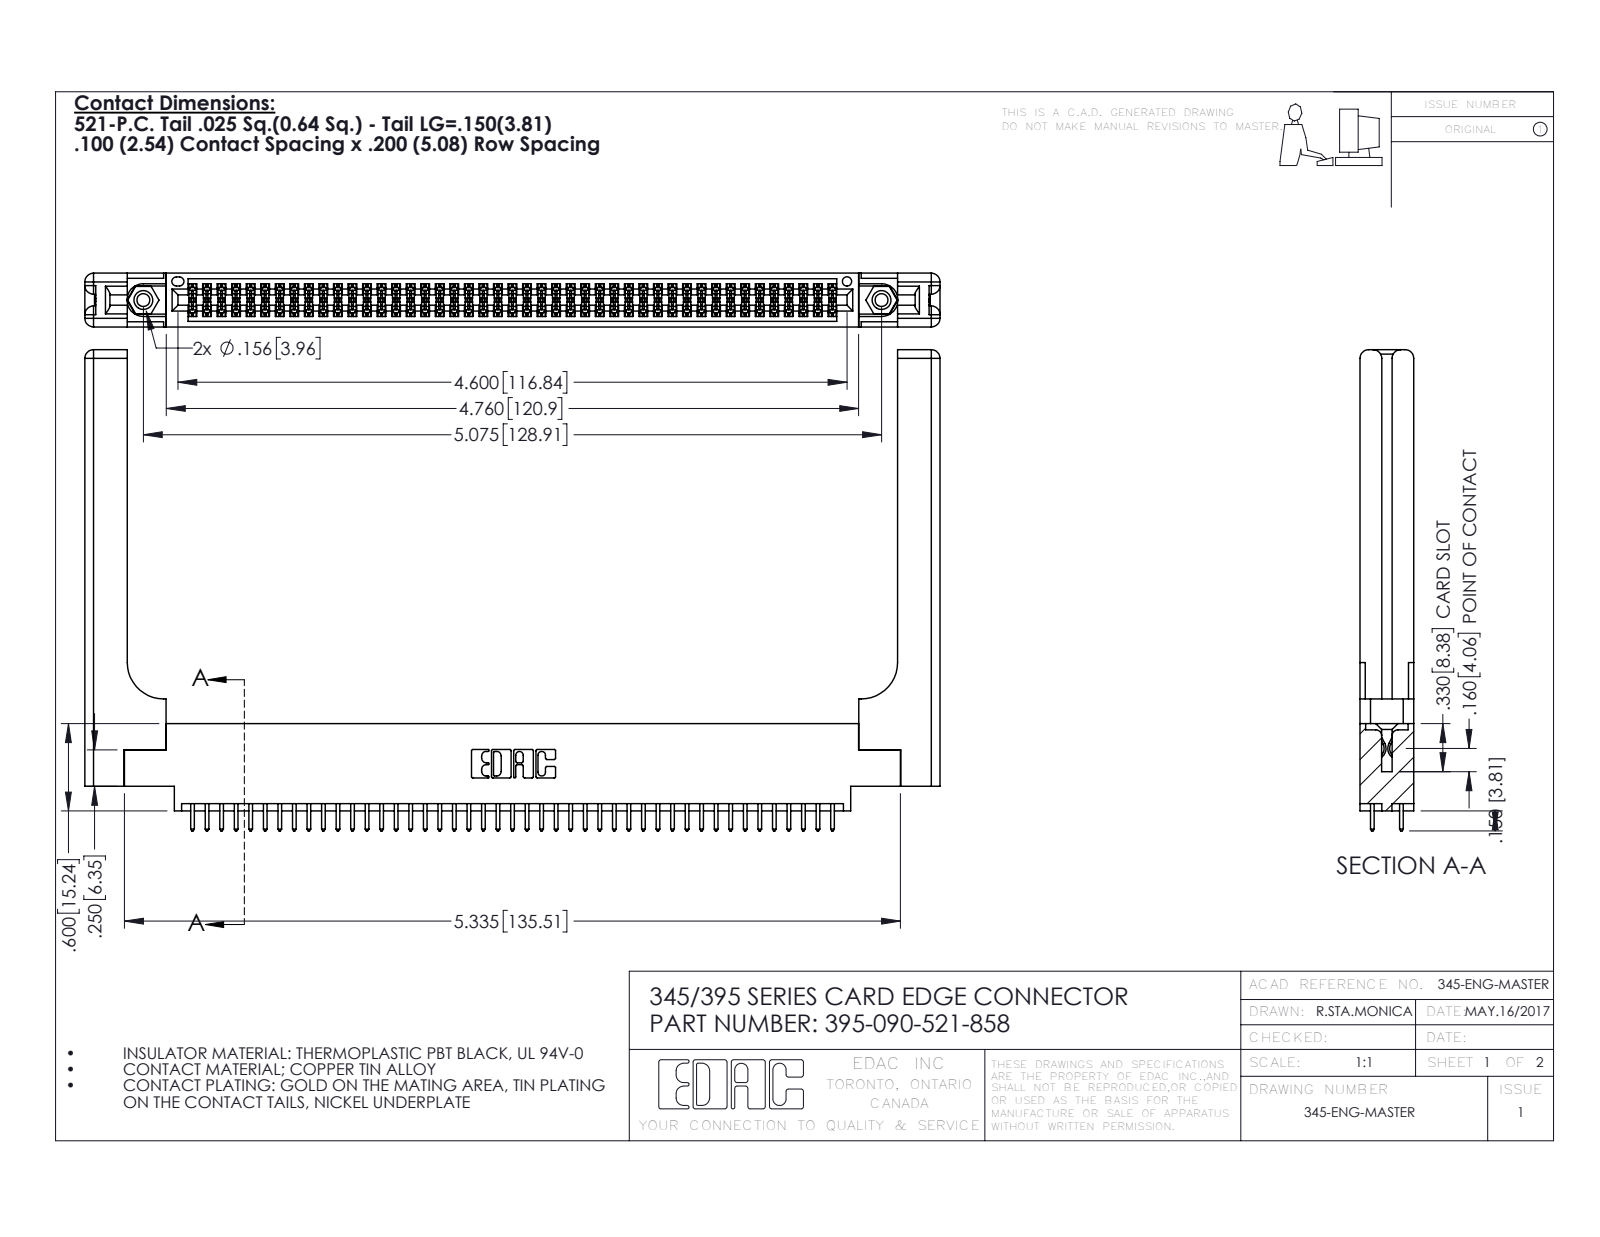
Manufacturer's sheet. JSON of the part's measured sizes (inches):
{"part_name": "345-292-001_345-293-121; 345-220-058_345-220-058; 345-250-001_345-250-001-102; 395-090-521-858 (+1 more)", "step_written_by": "SolidWorks 2016 (CONFIG_CONTROL_DESIGN)", "units": "inches", "bodies": {"solids": 95, "faces": 4886, "planar": 3202, "cylindrical": 1624, "other": 60}, "overall_size": [5.879, 3.307, 0.37], "volume_in3": 1.395, "surface_area_in2": 40.74, "round_holes": [[0.089, 2], [0.125, 2], [0.156, 2], [0.064, 1]], "round_bosses_or_shafts": [[0.155, 2]], "partial_cylinders_radius": [[0.006, 135], [0.01, 90], [0.01, 22], [0.06, 16], [0.007, 6], [0.031, 6], [0.026, 3], [0.014, 2]], "face_to_face_distances": [0.072, 0.37, 0.298, 0.098, 0.272, 0.025, 0.2, 0.225, 0.175, 0.148], "hole_center_spacings": [0.27, 4.839, 5.075]}
